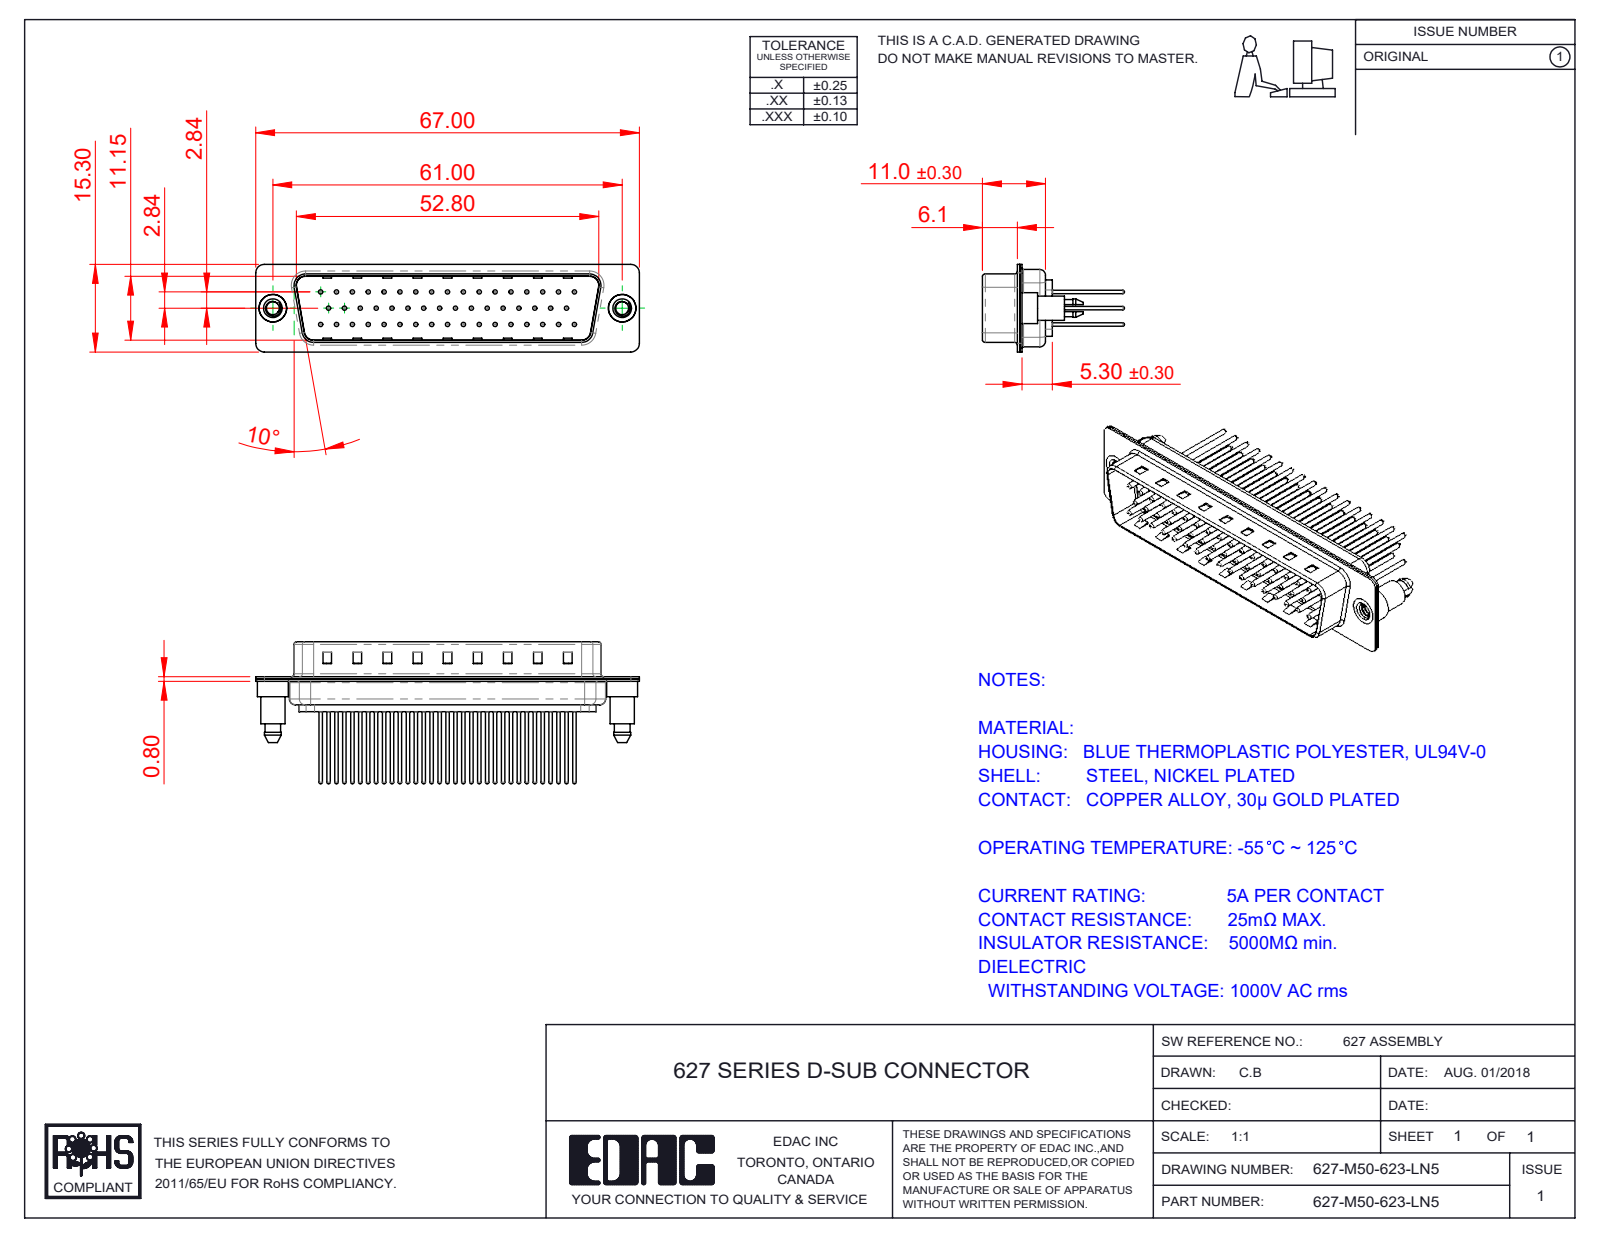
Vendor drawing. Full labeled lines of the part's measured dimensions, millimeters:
Part name (STEP PRODUCT): 627M Contact Row 2_23; 627M 4-40 Threaded Boardlock; 627M Housing_50 Contacts; 627-M50-623-LN5 (+4 more)
STEP written by: SolidWorks 2020 (CONFIG_CONTROL_DESIGN)
Units: millimetres
Bodies: 55 solids, 2312 faces (569 planar, 873 cylindrical, 870 other)
Overall size (bounding box): 67 × 24.77 × 15.3
Volume: 4 756 mm³ · Surface area: 11 680 mm²
Round holes (diameter × count): ⌀0.75 ×50, ⌀1.6 ×50, ⌀2 ×50, ⌀2.26 ×2, ⌀4 ×2, ⌀4.8 ×2
Round bosses / shafts (diameter × count): ⌀1.5 ×50, ⌀0.6 ×50, ⌀5.4 ×2, ⌀4.9 ×2, ⌀4.25 ×2
Partial cylindrical surfaces — rounded edges, fillets, slot ends (radius × count): R1.5 ×18, R2 ×12, R1.6 ×10, R0.5 ×8, R0.25 ×4, R0.6 ×4, R0.65 ×4, R0.9 ×4
Main face-to-face distances: 0.4, 11.55, 5.7, 6.1, 0.78, 0.77, 12.33, 5.3, 12.32, 13.1
Hole centre spacings: 3.16, 2.77, 5.54, 8.31, 11.08, 13.85, 16.62, 5.03
